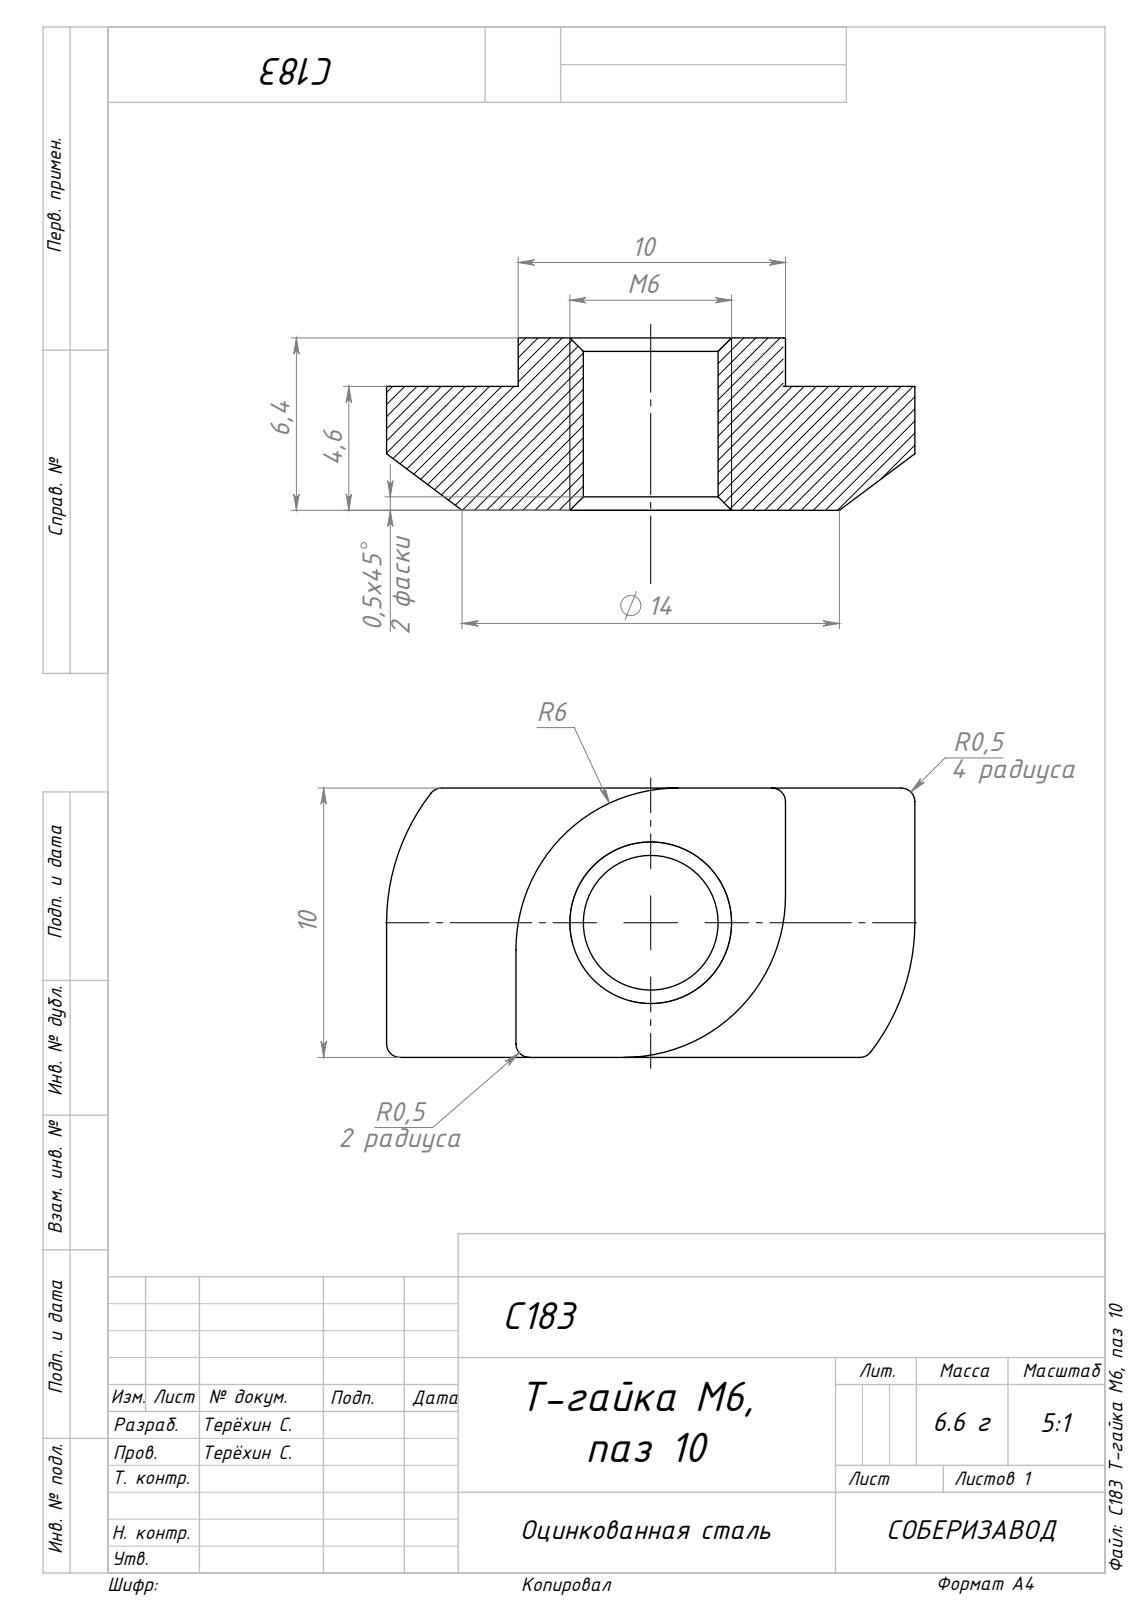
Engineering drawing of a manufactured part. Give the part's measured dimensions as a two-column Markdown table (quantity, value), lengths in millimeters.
| quantity | value |
| --- | --- |
| part name | C183 Т-гайка М6, паз 10_с резьбой; C183 Т-гайка М6, паз 10 |
| STEP written by | SolidWorks 2026 (CONFIG_CONTROL_DESIGN) |
| units | millimeters |
| bodies | 1 solid, 30 faces (12 planar, 12 cylindrical, 6 other) |
| overall size | 19.6 × 10 × 6.4 |
| volume | 839 mm³ |
| surface area | 713 mm² |
| round holes (diameter × count) | 5 × 1 |
| partial cylindrical surfaces (radius × count) | 0.5 × 6, 6 × 2, 7.84 × 2 |
| main face-to-face distances | 4.6, 10, 6.4, 1.8, 4.8, 14.8, 19.6 |
